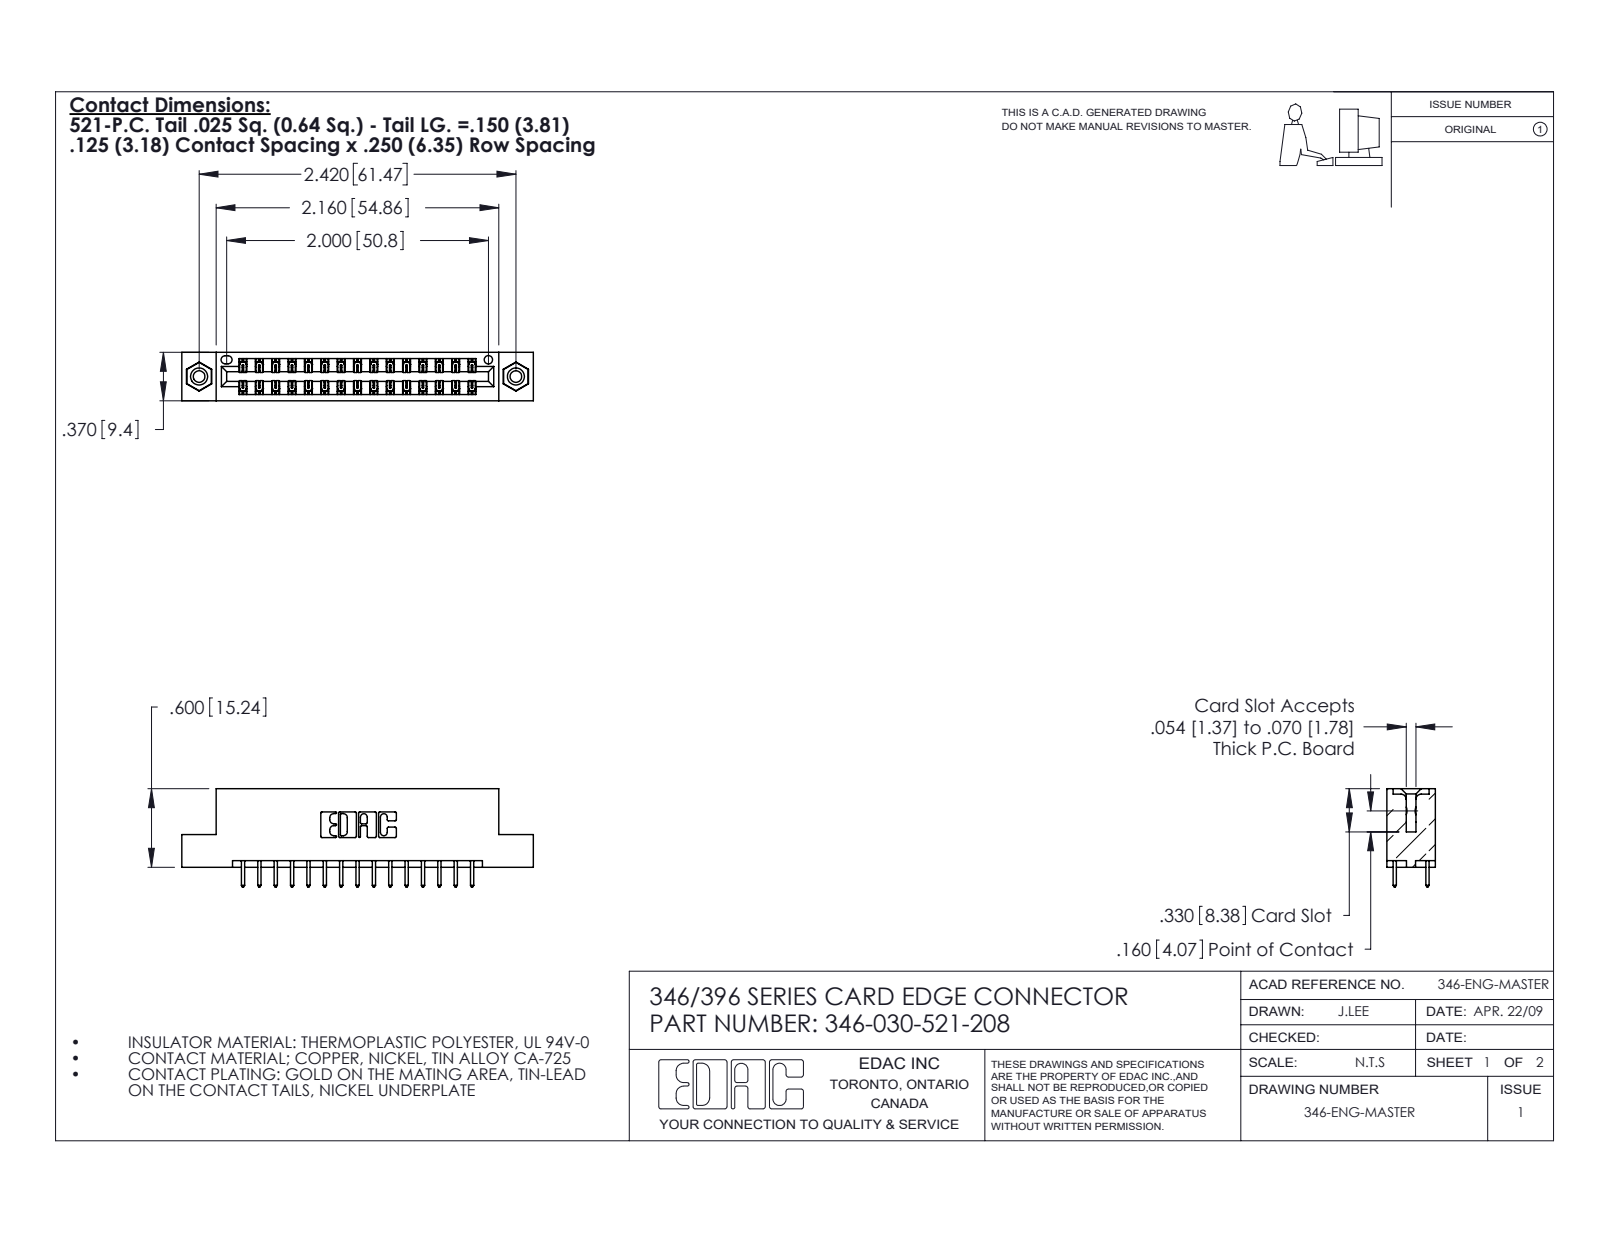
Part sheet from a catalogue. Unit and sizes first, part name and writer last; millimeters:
Units: millimetres
Overall size (bounding box): 68.2 × 19.1 × 9.4
Round holes (diameter × count): ⌀2.3 ×2, ⌀3.2 ×2, ⌀4 ×2, ⌀1.6 ×1
Round bosses / shafts (diameter × count): ⌀3.9 ×2
Partial cylindrical surfaces — rounded edges, fillets, slot ends (radius × count): R0.2 ×45, R0.3 ×30, R0.3 ×22, R0.2 ×6, R0.8 ×6, R0.7 ×3, R0.4 ×2, R0.6 ×2
Main face-to-face distances: 1.2, 8.2, 6.4, 9.4, 1.8, 7.6, 0.6, 7, 3.8, 5.6
Hole centre spacings: 6.2, 56.2, 61.5
Volume: 6 420 mm³ · Surface area: 8 342 mm²
Bodies: 33 solids, 1742 faces (1158 planar, 568 cylindrical, 16 other)
Part name (STEP PRODUCT): 345-292-001_345-293-121; 346-030-521-208; 346 Part_Flush Mounting Lugs - 0.156 Dia-TI; 345-250-001_345-250-003-102
STEP written by: SolidWorks 2020 (CONFIG_CONTROL_DESIGN)
